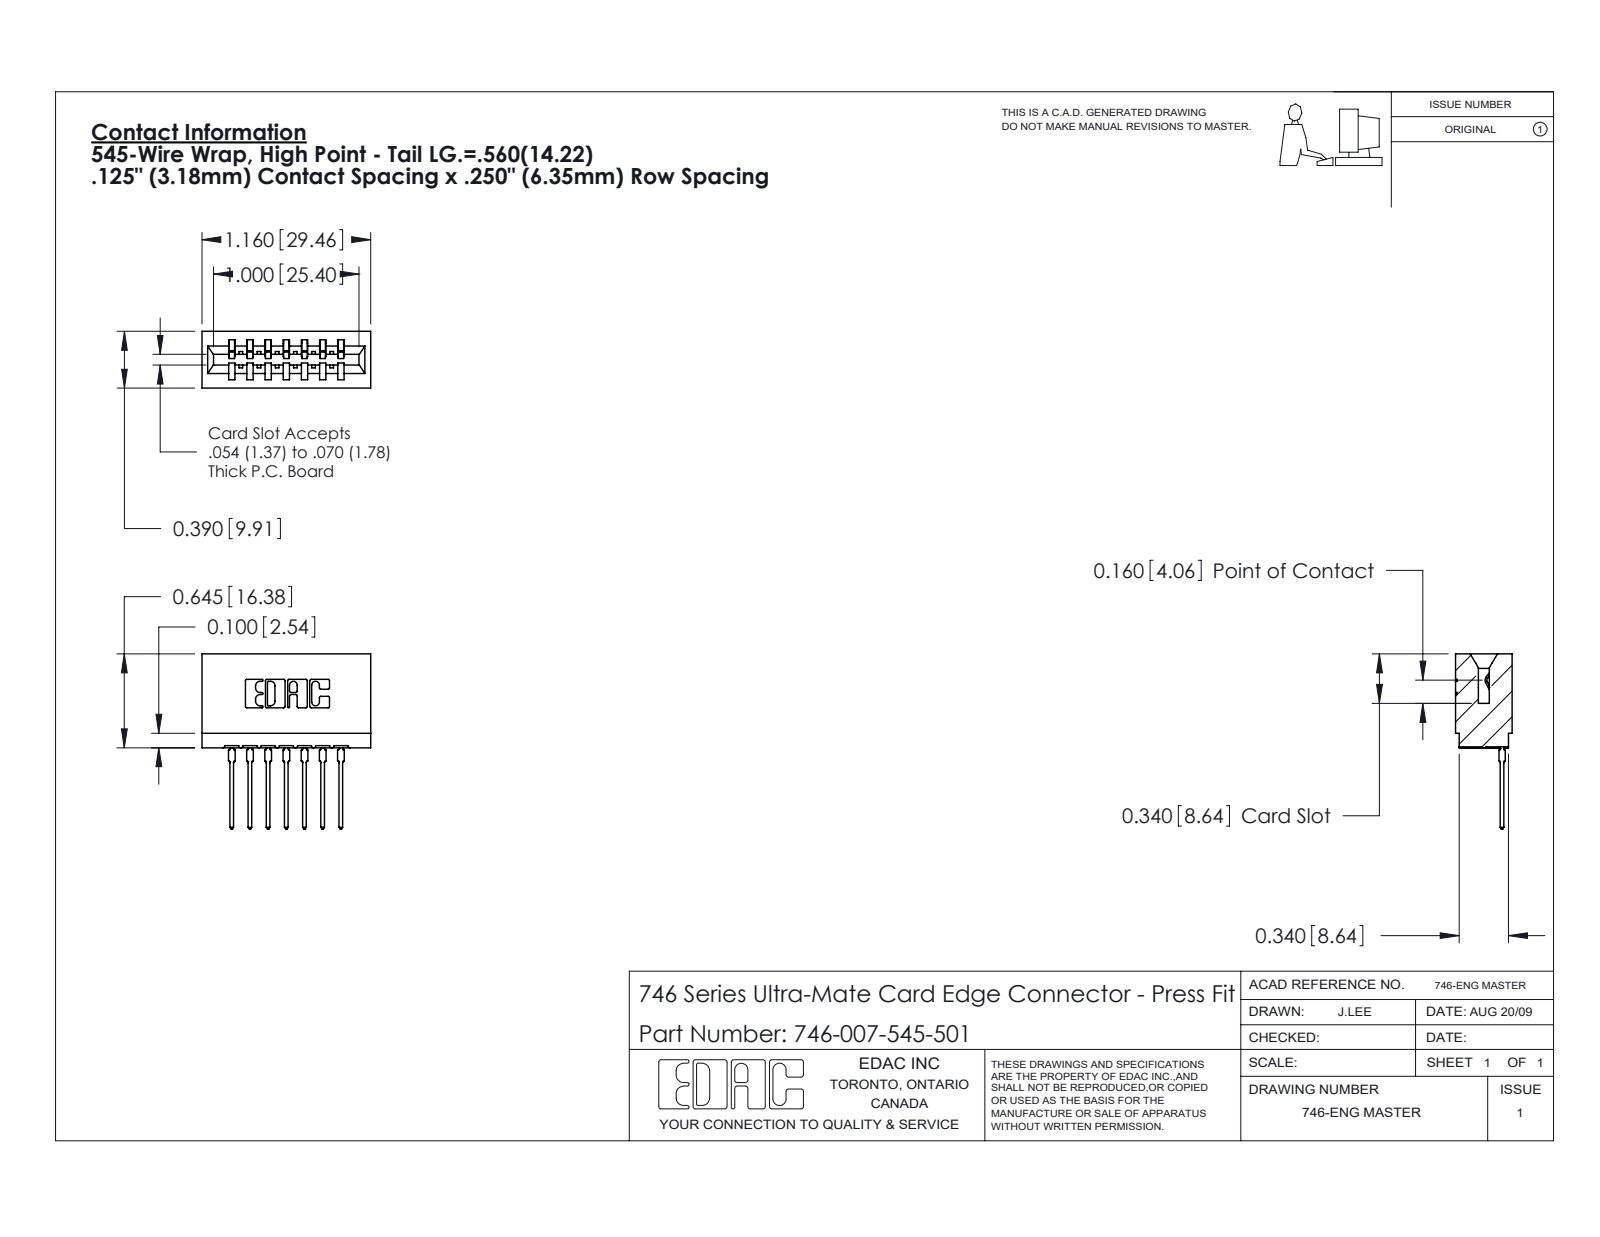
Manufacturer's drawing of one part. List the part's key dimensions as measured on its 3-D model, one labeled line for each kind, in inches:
Part name (STEP PRODUCT): 746 Part_.340 Slot Depth - 01; 746-292-001_545; 746-007-545-501
STEP written by: SolidWorks 2020 (CONFIG_CONTROL_DESIGN)
Units: inches
Bodies: 8 solids, 853 faces (496 planar, 175 cylindrical, 182 other)
Overall size (bounding box): 1.204 × 1.16 × 0.39
Volume: 0.216 in³ · Surface area: 6.729 in²
Partial cylindrical surfaces — rounded edges, fillets, slot ends (radius × count): R0.01 ×22, R0.021 ×14, R0.015 ×8, R0.007 ×6, R0.031 ×6, R0.005 ×4, R0.011 ×4, R0.026 ×3
Main face-to-face distances: 0.25, 0.042, 0.333, 0.125, 0.125, 0.5, 0.057, 0.292, 0.208, 0.39
